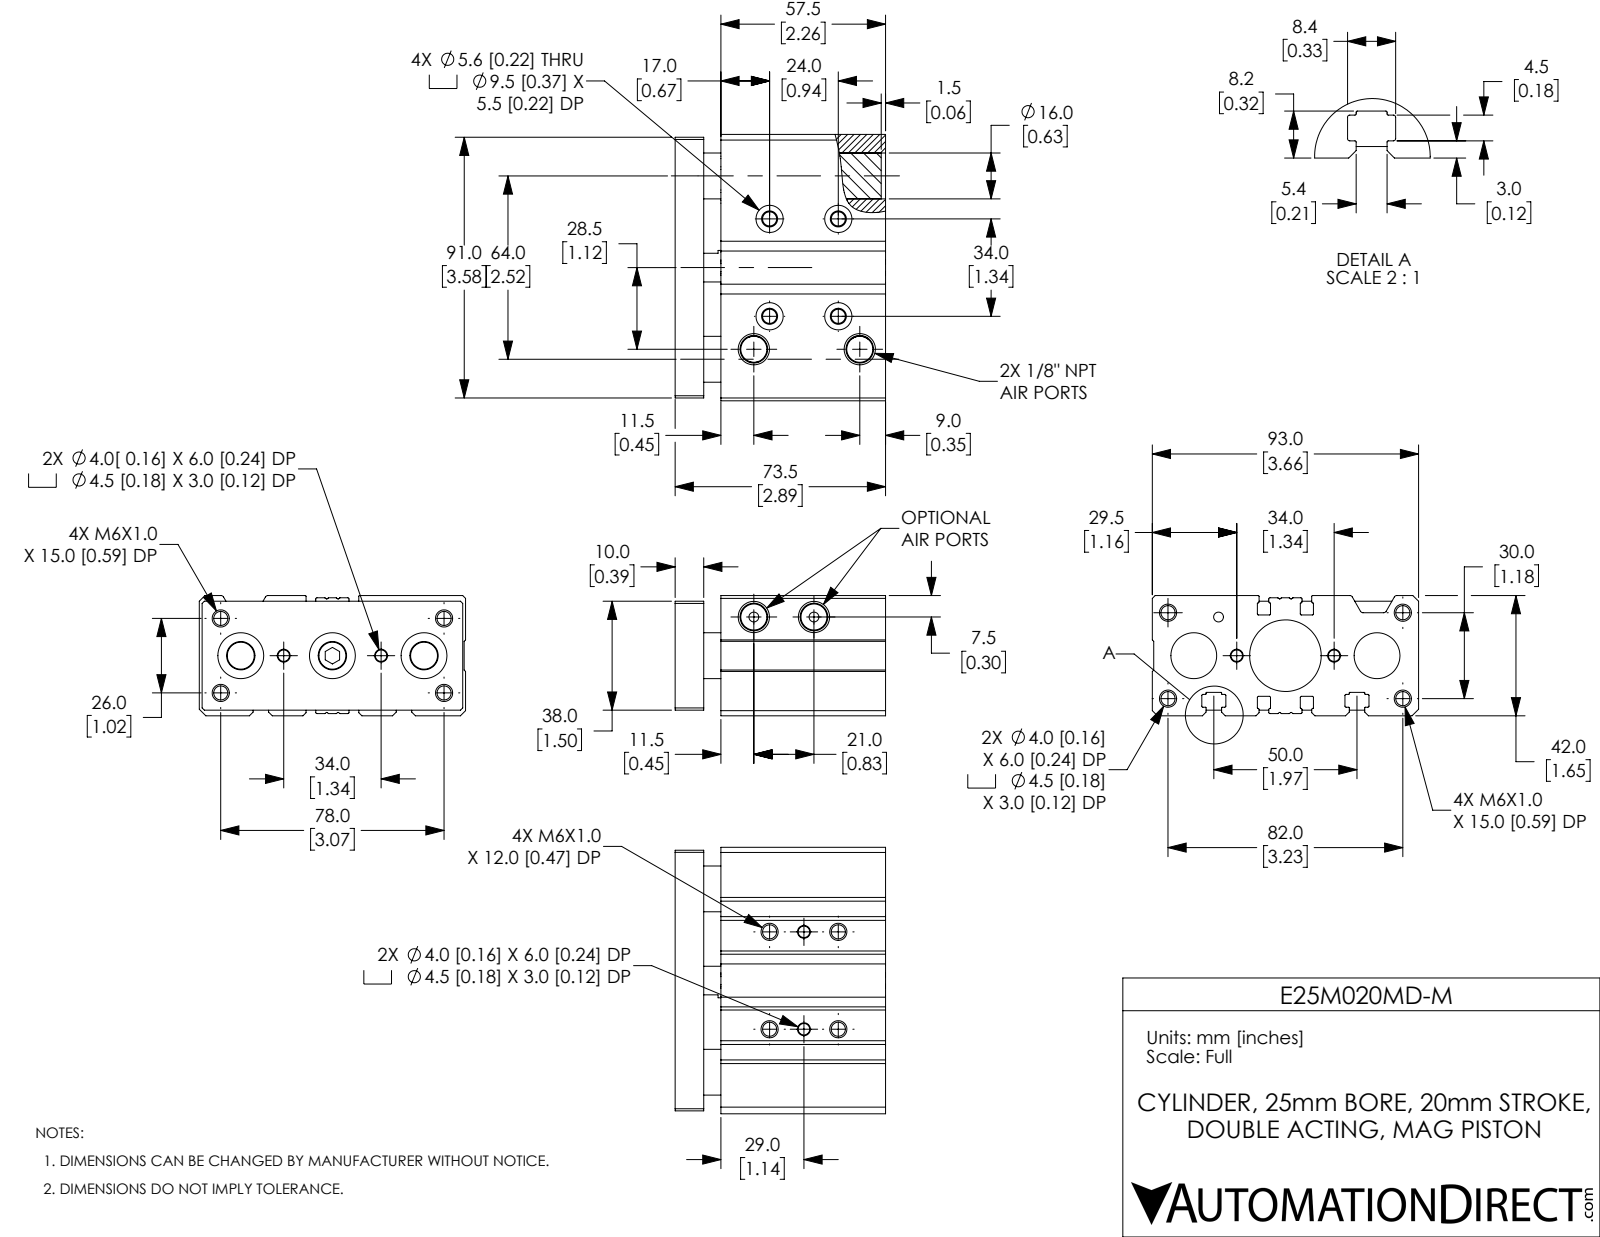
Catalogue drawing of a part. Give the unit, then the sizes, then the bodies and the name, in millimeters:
Units: millimetres
Overall size (bounding box): 93 × 73.5 × 42
Round holes (diameter × count): ⌀4.92 ×8, ⌀4 ×4, ⌀4.5 ×4, ⌀4.92 ×4, ⌀5.6 ×4, ⌀9.5 ×4, ⌀3.43 ×3, ⌀8 ×3, ⌀16 ×3, ⌀9.91 ×2, ⌀16 ×1, ⌀25 ×1
Round bosses / shafts (diameter × count): ⌀12 ×1, ⌀9.91 ×1
Partial cylindrical surfaces — rounded edges, fillets, slot ends (radius × count): R0.2 ×32, R0.4 ×28, R1 ×4, R0.3 ×2
Main face-to-face distances: 6, 16, 10, 42, 2, 73.5, 63.5, 57.5, 40, 8
Hole centre spacings: 2.83, 12, 14.76, 17.49, 25.55, 28.07, 28.3, 34
Volume: 222 002 mm³ · Surface area: 67 101 mm²
Bodies: 5 solids, 423 faces (139 planar, 190 cylindrical, 94 other)
Part name (STEP PRODUCT): E25M020MD-M_BODY; E25M020MD-M_ENDPLATE; E25M020MD-M
STEP written by: SolidWorks 2019 (CONFIG_CONTROL_DESIGN)
